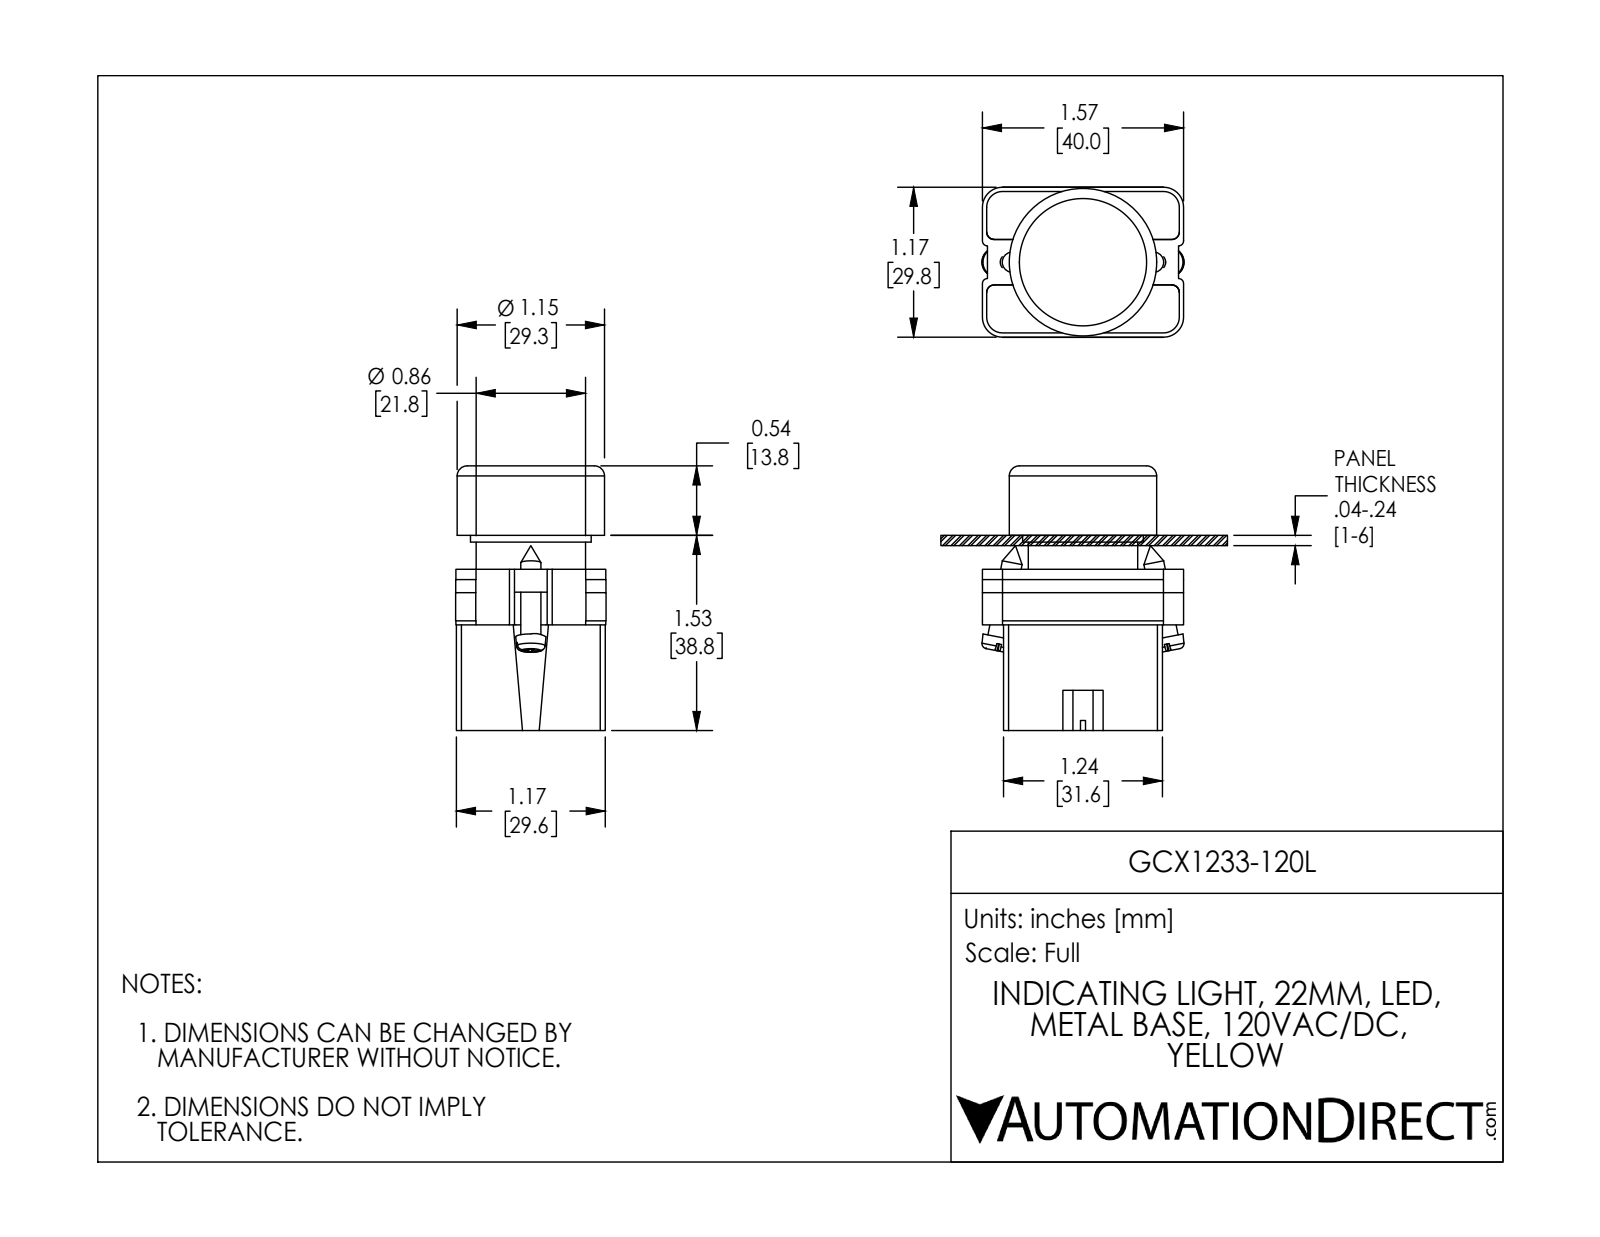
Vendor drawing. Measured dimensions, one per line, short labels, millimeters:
name: ECX1050; GCX1233L OPERATOR; ecx1029; GCX1233-120L
written by: SolidWorks 2016 (AUTOMOTIVE_DESIGN)
unit: mm
bodies: 7 solids, 339 faces (178 planar, 134 cylindrical, 27 other)
size: 52.6 × 40.2 × 29.9
volume: 37 170 mm³; area: 20 120 mm²
holes: 2× ⌀3.1, 2× ⌀3.3, 1× ⌀5, 1× ⌀11.9, 1× ⌀21.6, 1× ⌀22.3, 1× ⌀22.6, 1× ⌀28
bosses: 4× ⌀4, 1× ⌀29.3, 1× ⌀27.7, 1× ⌀24, 1× ⌀21.7, 1× ⌀19.8, 1× ⌀12.8
rounds: 24× R1.5, 12× R1, 12× R3.1, 12× R4, 8× R1, 2× R3.3, 1× R10, 1× R10.1
face distances: 21.8, 31.6, 21, 42.8, 28.9, 0.8, 49.9, 7, 0.8, 29.6
